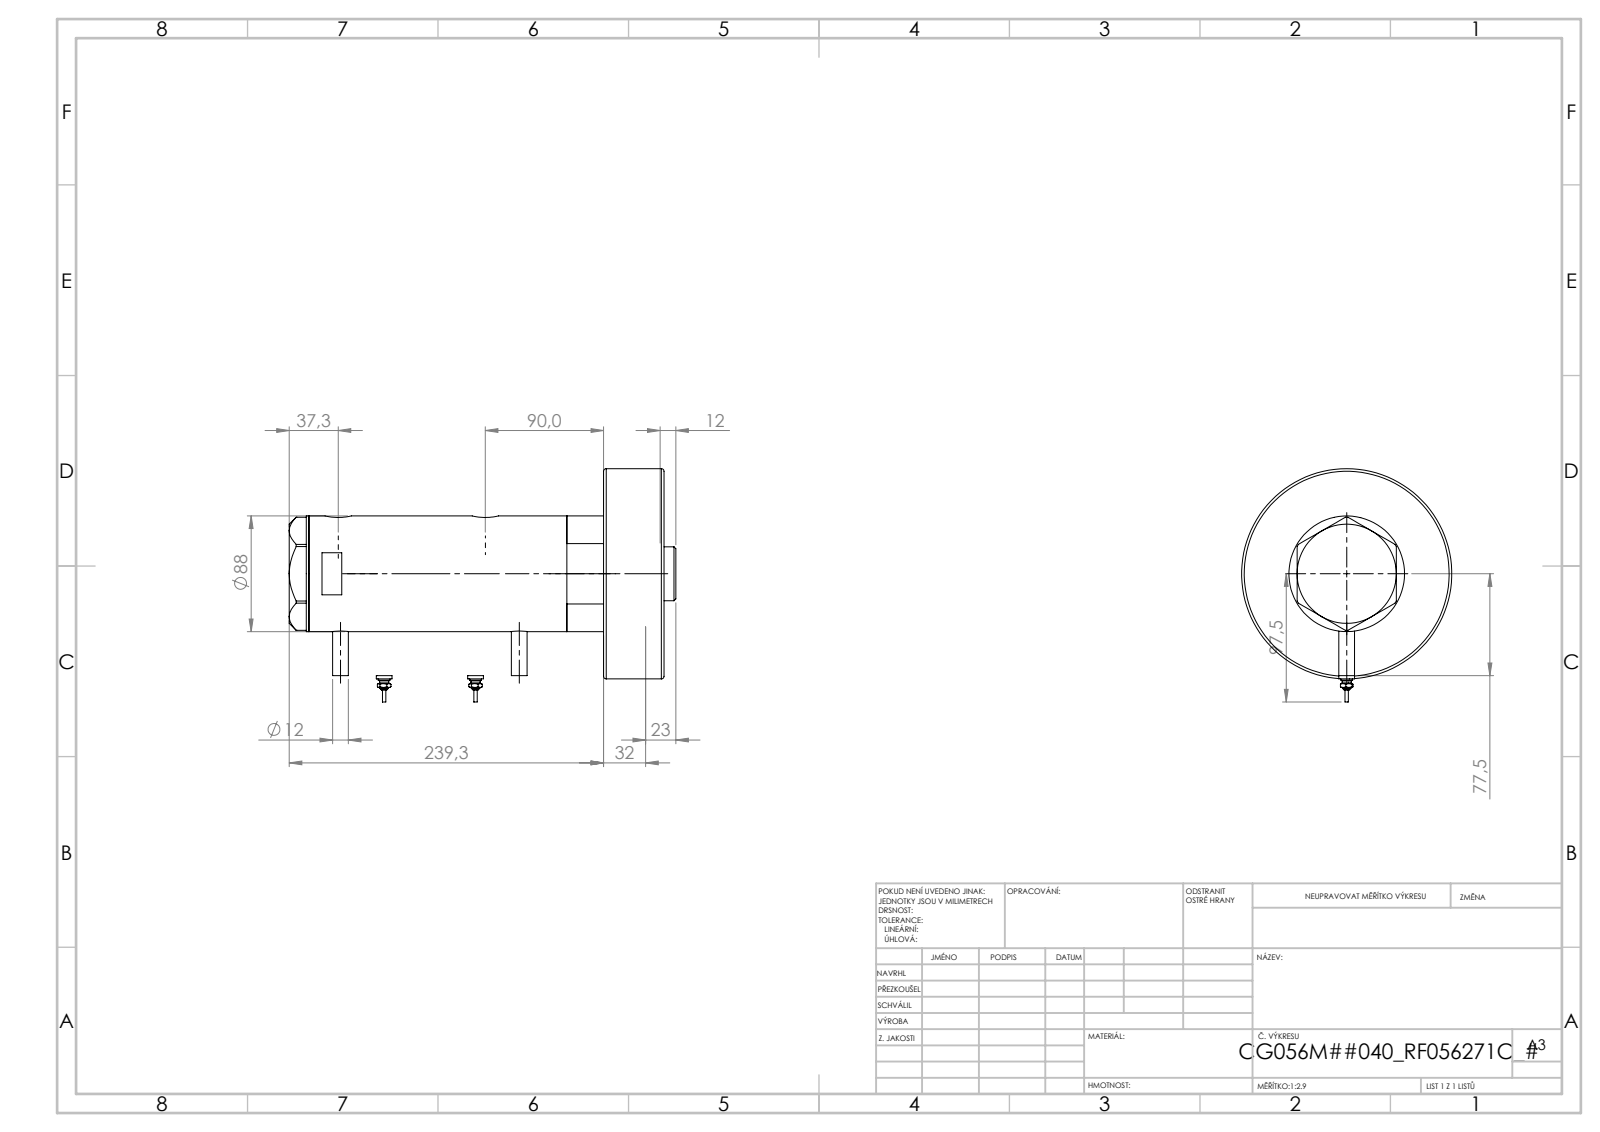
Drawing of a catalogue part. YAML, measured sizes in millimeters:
part_name: "V270CG_VC; V270CG_271C; V270CG_SWITCH; V270CG_MIDDLE (+2 more)"
step_written_by: "SolidWorks 2019 (CONFIG_CONTROL_DESIGN)"
units: millimeters
bodies: {solids: 7, faces: 242, planar: 83, cylindrical: 81, other: 78}
overall_size: [264.47, 160, 160]
volume: 2086000
surface_area: 270051
round_holes:
  - {diameter: 5, count: 2}
  - {diameter: 12.5, count: 2}
  - {diameter: 13.16, count: 2}
  - {diameter: 20, count: 2}
  - {diameter: 14.5, count: 1}
  - {diameter: 42, count: 1}
  - {diameter: 43.5, count: 1}
  - {diameter: 56, count: 1}
  - {diameter: 60, count: 1}
  - {diameter: 75, count: 1}
  - {diameter: 80, count: 1}
round_bosses_or_shafts:
  - {diameter: 12, count: 2}
  - {diameter: 9, count: 2}
  - {diameter: 7, count: 2}
  - {diameter: 4.34, count: 2}
  - {diameter: 2.4, count: 2}
  - {diameter: 160, count: 1}
  - {diameter: 88, count: 1}
  - {diameter: 73, count: 1}
face_to_face_distances: [46, 191.9, 237.9, 114.4, 77.5, 123.5, 26, 88.4, 165.9, 211.9]
hole_center_spacings: [1.7, 25.8, 90.3, 92, 116.1, 117.8]
